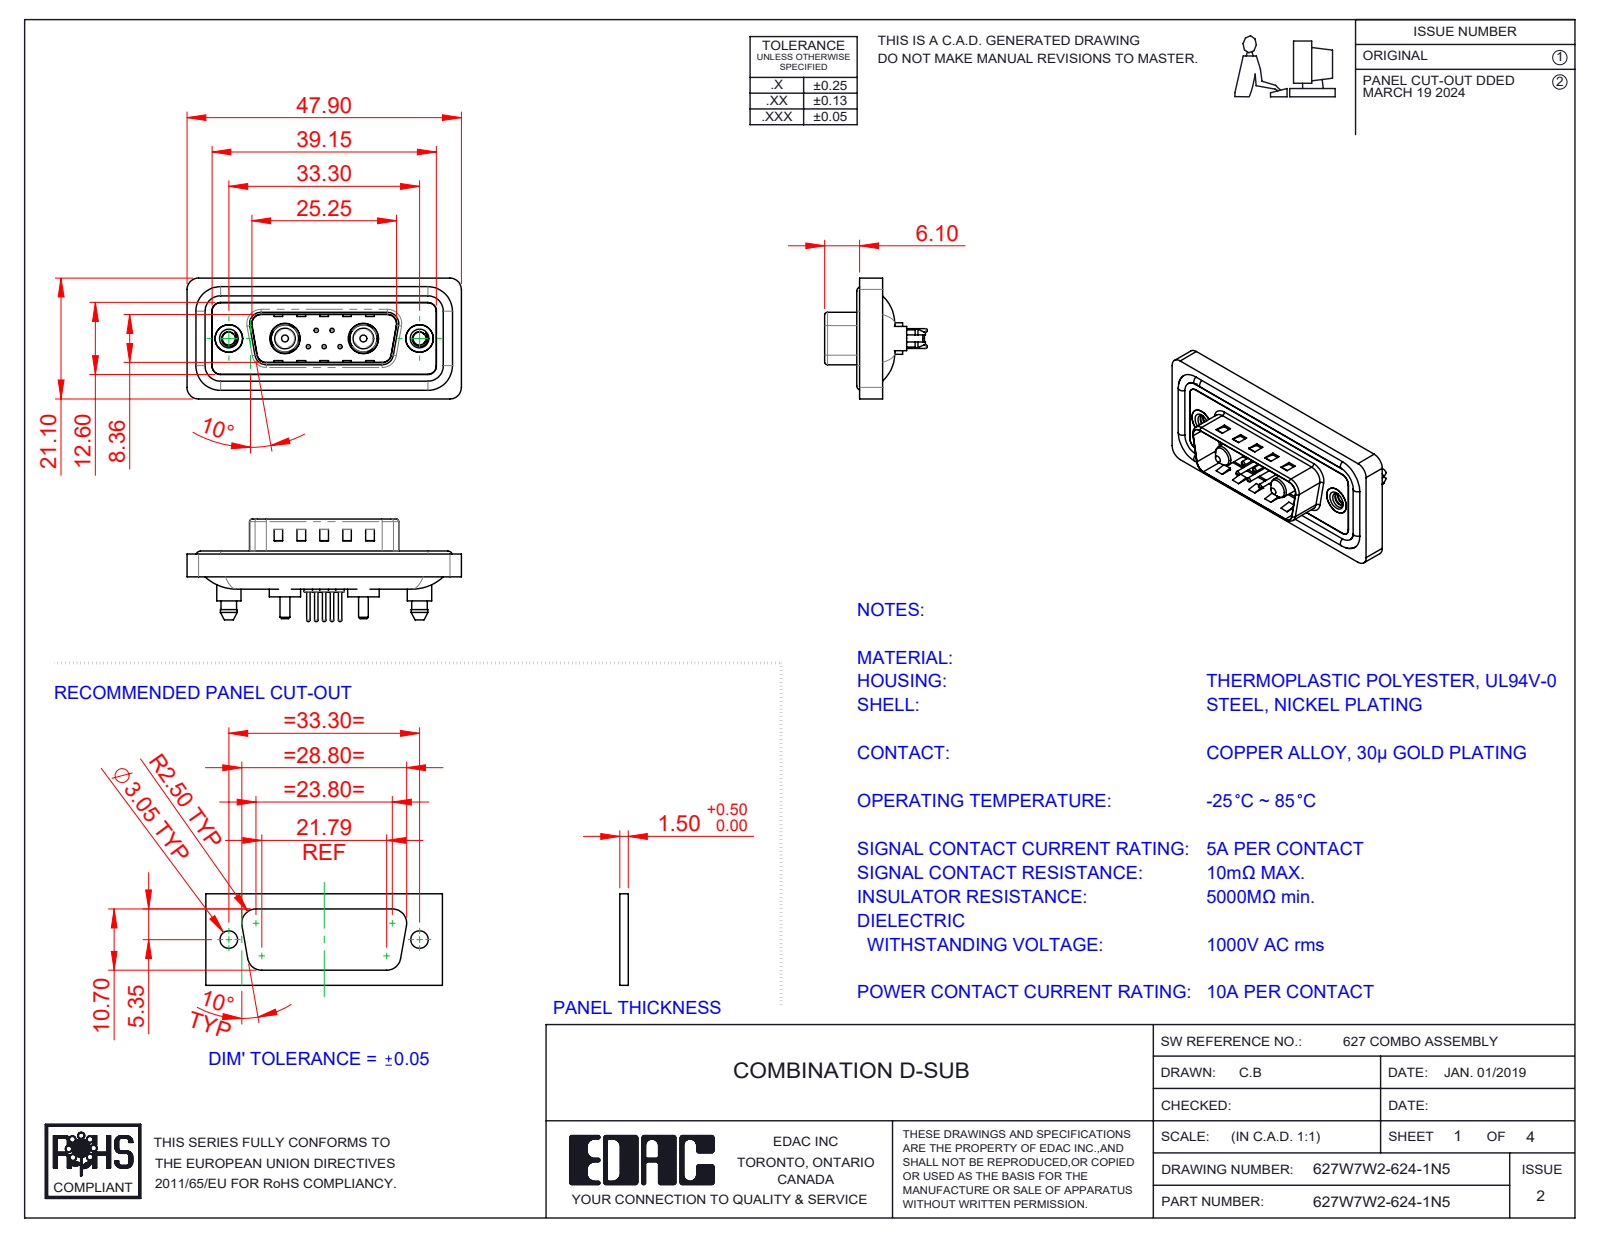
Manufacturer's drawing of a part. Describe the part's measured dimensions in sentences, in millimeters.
The part is named "627Combo Shell Front_15 Contacts; 627Combo Shell Rear_15 Contacts; 627Combo Waterproof Housing_15 Contacts; 627Combo Contact Row 2_24 (+5 more)". Its 3-D file was written by "SolidWorks 2023 (CONFIG_CONTROL_DESIGN)". It is 16 solids with 760 faces: 248 planar, 324 cylindrical and 188 other. Overall it measures 47.9 by 21.1 by 17.9 millimeters. Its volume is 5 621 cubic millimeters and its surface area 9 101 square millimeters. Round holes: 5 of diameter 0.75, 5 of diameter 1.6, 5 of diameter 2, 2 of diameter 2.26, 2 of diameter 4, 2 of diameter 4.8, 2 of diameter 4.85, 2 of diameter 5, 2 of diameter 5.3. Round bosses or shafts: 5 of diameter 1.5, 5 of diameter 0.6, 4 of diameter 1.6, 2 of diameter 5.5, 2 of diameter 5.4, 2 of diameter 5.2, 2 of diameter 4.9, 2 of diameter 4.75. Partial cylindrical surfaces (rounded edges, fillets, slot ends): 28 of radius 1.5, 20 of radius 2, 10 of radius 1.6, 8 of radius 0.5, 4 of radius 0.25, 4 of radius 0.6, 4 of radius 0.65, 4 of radius 0.9. The main face-to-face distances are 0.4, 1.1, 1.5, 1.6, 0.5, 3.1, 2.9, 4, 0.7, 0.82. The hole center spacings are 3.16, 2.77, 9.8, 23.5, 4.31, 4.33, 5.03, 5.04.
